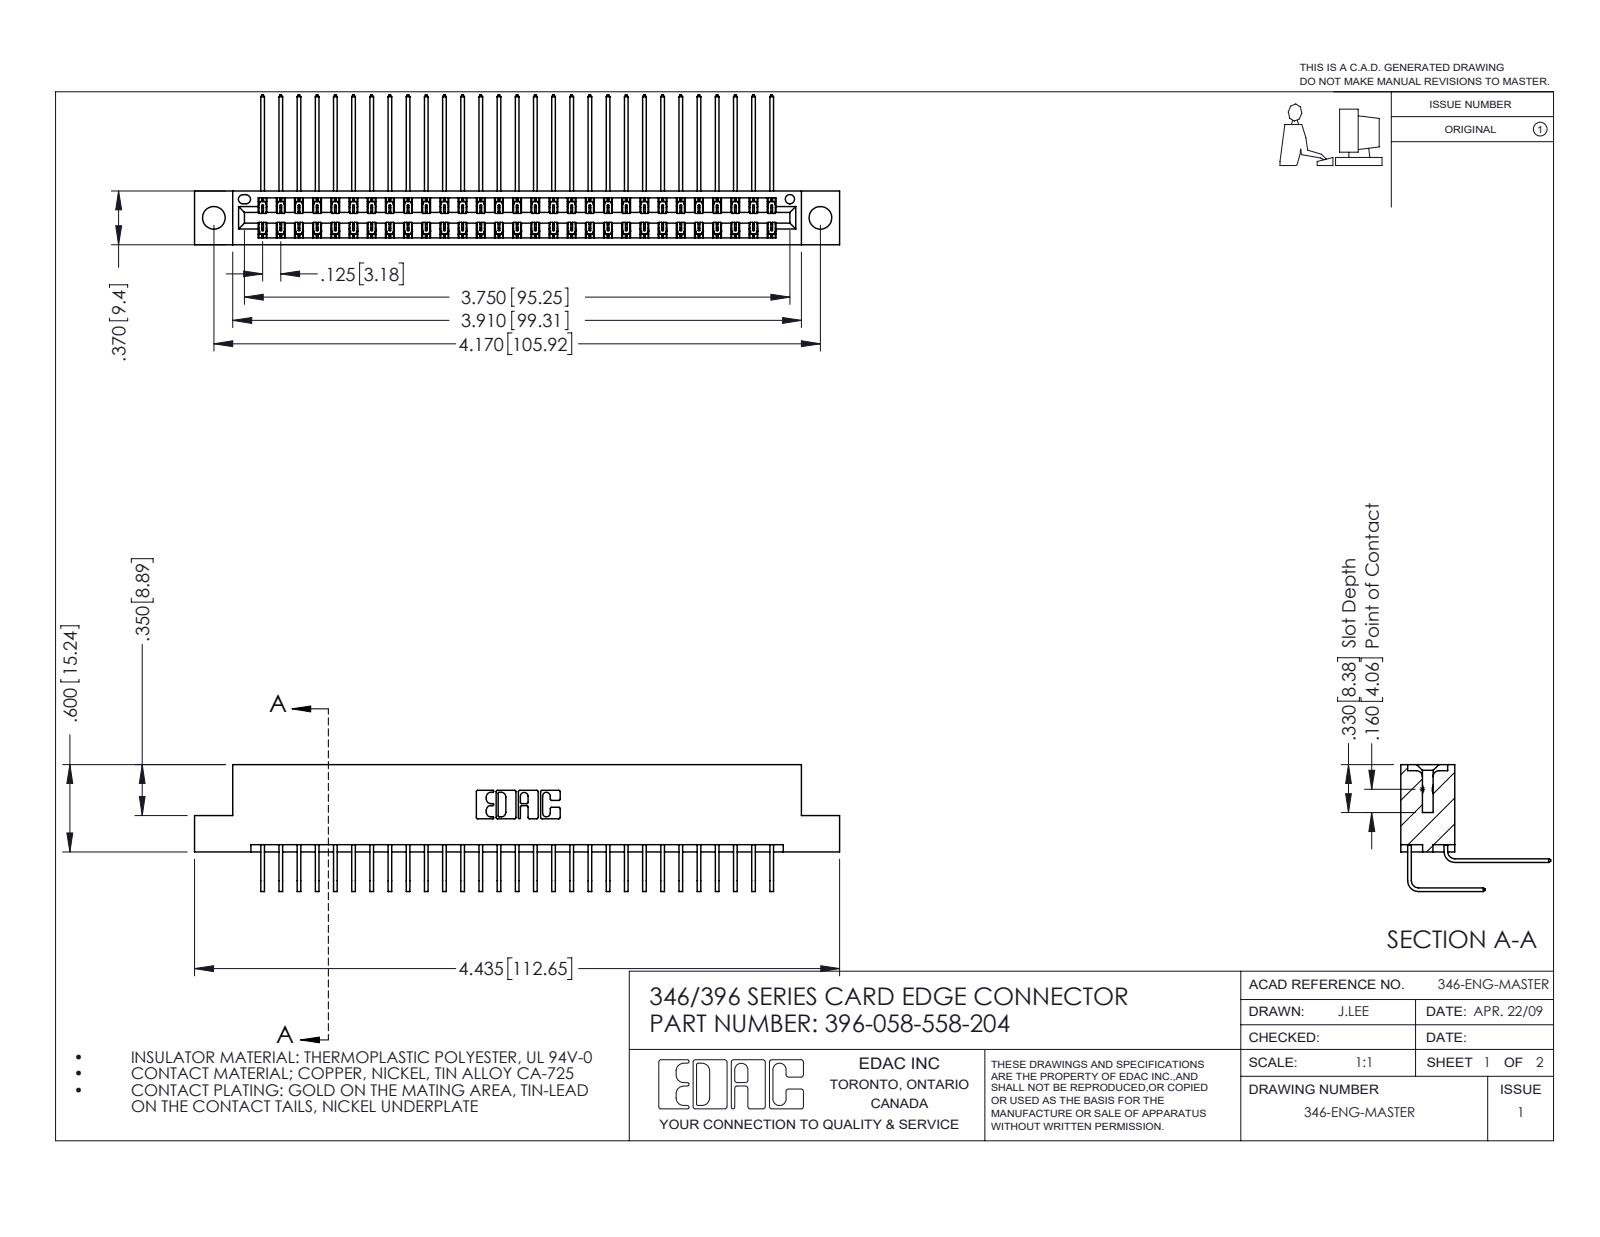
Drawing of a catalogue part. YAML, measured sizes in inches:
part_name: "396-058-558-204; 346 Part_Flush Mounting Lugs - 0.156 Dia-TH; 345-292-001_558 559 Tail - 1; 345-292-001_558 Tail - 2"
step_written_by: "SolidWorks 2016 (CONFIG_CONTROL_DESIGN)"
units: inches
bodies: {solids: 59, faces: 3254, planar: 2222, cylindrical: 1032, other: 0}
overall_size: [4.435, 1.03, 0.873]
volume: 0.679
surface_area: 25.6
round_holes:
  - {diameter: 0.156, count: 2}
  - {diameter: 0.064, count: 1}
partial_cylinders:
  - {radius: 0.006, count: 87}
  - {radius: 0.01, count: 22}
  - {radius: 0.007, count: 6}
  - {radius: 0.031, count: 6}
  - {radius: 0.026, count: 3}
  - {radius: 0.014, count: 2}
  - {radius: 0.022, count: 2}
  - {radius: 0.024, count: 2}
face_to_face_distances: [0.322, 0.048, 0.025, 0.25, 0.37, 0.298, 0.072, 0.275, 0.148, 0.222]
hole_center_spacings: [0.246, 3.962, 4.17]
